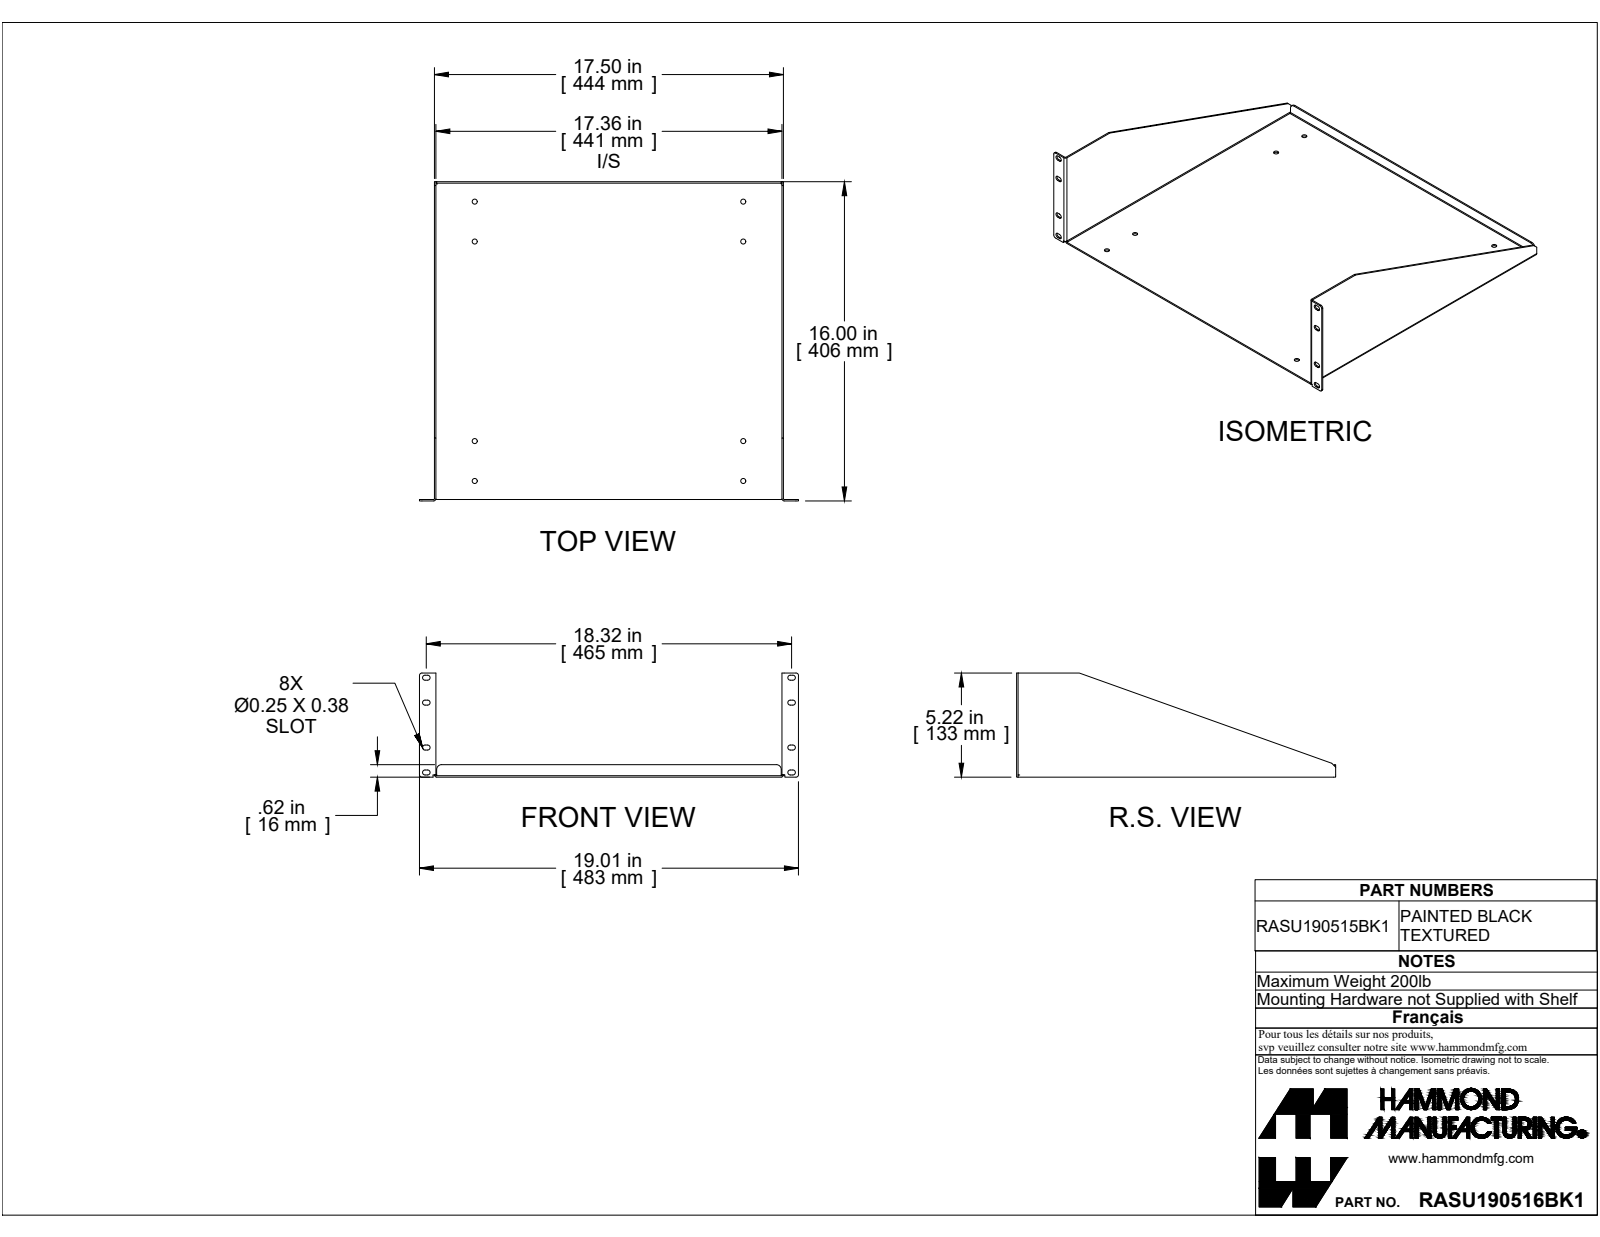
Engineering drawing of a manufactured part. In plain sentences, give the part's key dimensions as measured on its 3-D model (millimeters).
The part is named "RASU190516BK1". Its 3-D file was written by "SolidWorks 2019 (CONFIG_CONTROL_DESIGN)". It is 1 solid with 96 faces: 56 planar, 40 cylindrical and 0 other. Overall it measures 482.8 by 406.4 by 132.5 millimeters. Its volume is 470 600 cubic millimeters and its surface area 519 200 square millimeters. Round holes: 8 of diameter 6.4. Partial cylindrical surfaces (rounded edges, fillets, slot ends): 20 of radius 3.2, 5 of radius 0.9, 5 of radius 2.7, 2 of radius 6.4. The main face-to-face distances are 1.8, 442.7, 440.8, 444.5, 402.7, 404.6, 1.8, 404.6, 406.4, 15.9. The hole center spacings are 50.8, 304.8, 342.1, 345.8, 458.2, 254, 355.6, 426.1.
